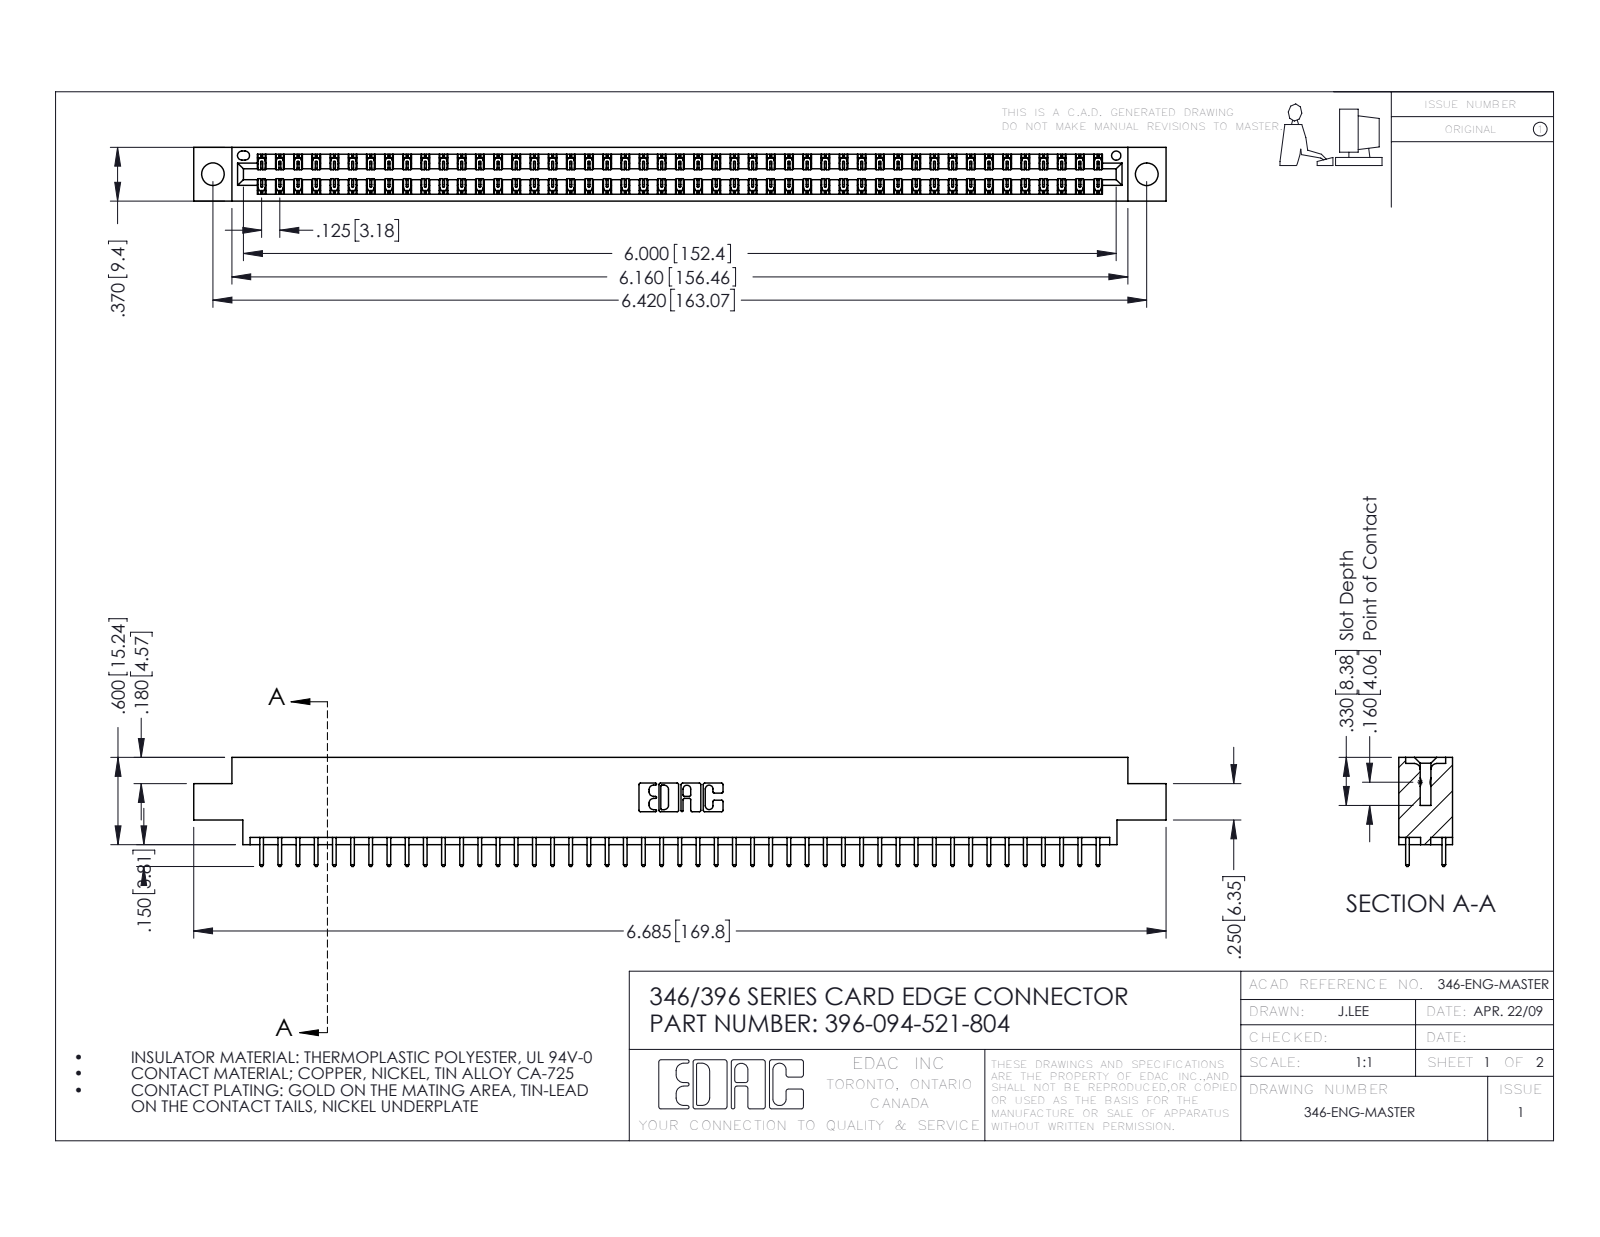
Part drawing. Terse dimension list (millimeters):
name: 396-094-521-804; 346 Part_0.170 Offset - 0.156 Dia-TH; 345-292-001_345-293-121
written by: SolidWorks 2016 (CONFIG_CONTROL_DESIGN)
unit: mm
bodies: 95 solids, 5014 faces (3370 planar, 1644 cylindrical, 0 other)
size: 169.8 × 19.1 × 9.4
volume: 16 300 mm³; area: 22 240 mm²
holes: 2× ⌀4, 1× ⌀1.6
rounds: 141× R0.2, 94× R0.3, 22× R0.3, 6× R0.2, 6× R0.8, 3× R0.7, 2× R0.4, 2× R0.6
face distances: 1.2, 8.2, 9.4, 6.4, 1.8, 7.6, 0.6, 7, 3.8, 5.6
hole spacings: 6.2, 157.8, 163.1
